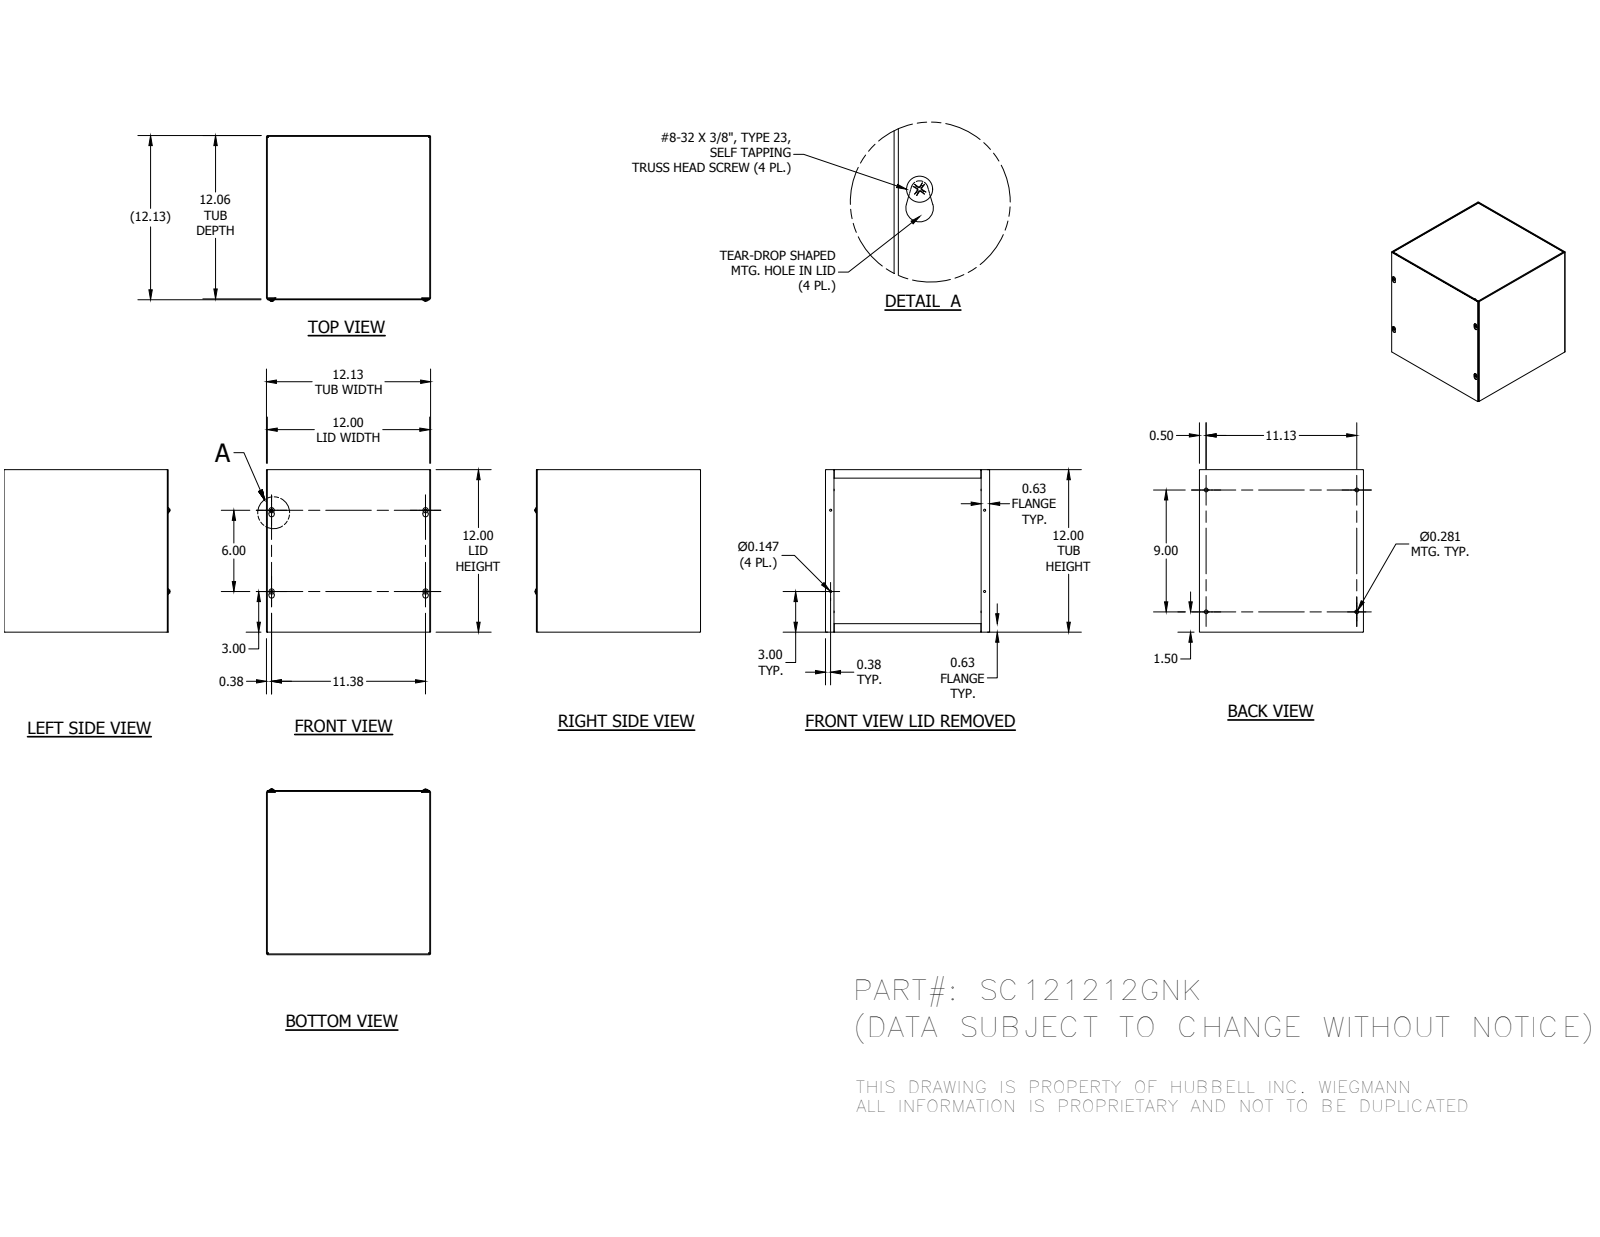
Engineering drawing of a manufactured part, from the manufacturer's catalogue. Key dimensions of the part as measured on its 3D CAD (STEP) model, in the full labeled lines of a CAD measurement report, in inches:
Part name (STEP PRODUCT): SC121212GNKBLR; SC1212GNKTB; SC1212GLPA; 34056 (+1 more)
STEP written by: Autodesk Inventor 2014 (AUTOMOTIVE_DESIGN)
Units: inches
Bodies: 8 solids, 268 faces (152 planar, 48 cylindrical, 68 other)
Overall size (bounding box): 12.225 × 12.125 × 12
Volume: 58 in³ · Surface area: 1 872 in²
Round holes (diameter × count): ⌀0.147 ×4, ⌀0.281 ×4
Round bosses / shafts (diameter × count): ⌀0.384 ×4, ⌀0.164 ×4
Partial cylindrical surfaces — rounded edges, fillets, slot ends (radius × count): R0.016 ×12, R0.078 ×12, R0.125 ×4, R0.203 ×4
Main face-to-face distances: 0.063, 12, 12.063, 11.937, 0.062, 11.875, 12.062, 12.125, 12.125, 0.125
Hole centre spacings: 1.505, 7.501, 11.35, 13.521, 6, 9, 11.125, 11.375
